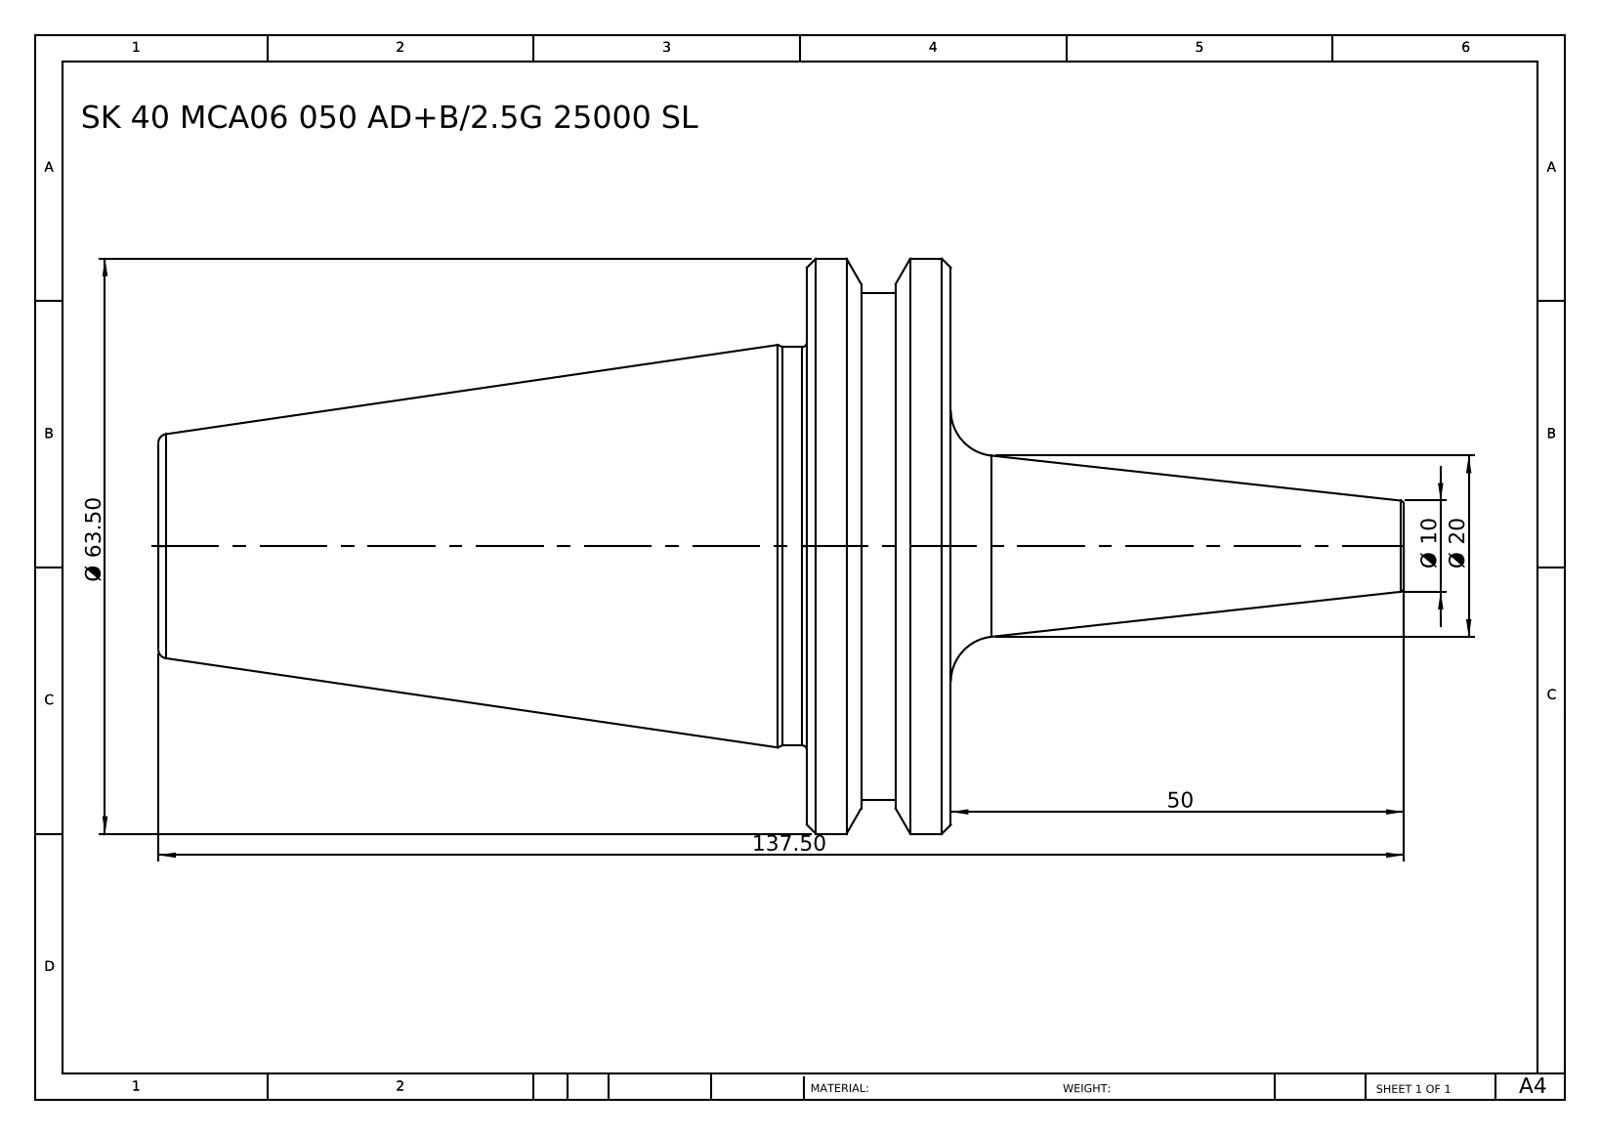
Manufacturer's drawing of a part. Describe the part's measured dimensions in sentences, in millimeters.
The part is named "SK 40 MCA06 050 AD+B-2.5G 25000 SL". Its 3-D file was written by "SolidWorks 2014 (CONFIG_CONTROL_DESIGN)". It is 1 solid with 36 faces: 6 planar, 8 cylindrical and 22 other. Overall it measures 137.5 by 63.5 by 63.5 millimeters. Its volume is 127 212 cubic millimeters and its surface area 19 016 square millimeters. Round bosses or shafts: 1 of diameter 63.5, 1 of diameter 56, 1 of diameter 44. The main face-to-face distances are 15.9, 87.5, 71.6, 9.9, 6, 77.6, 6.1, 3.8, 9.8, 81.4.
